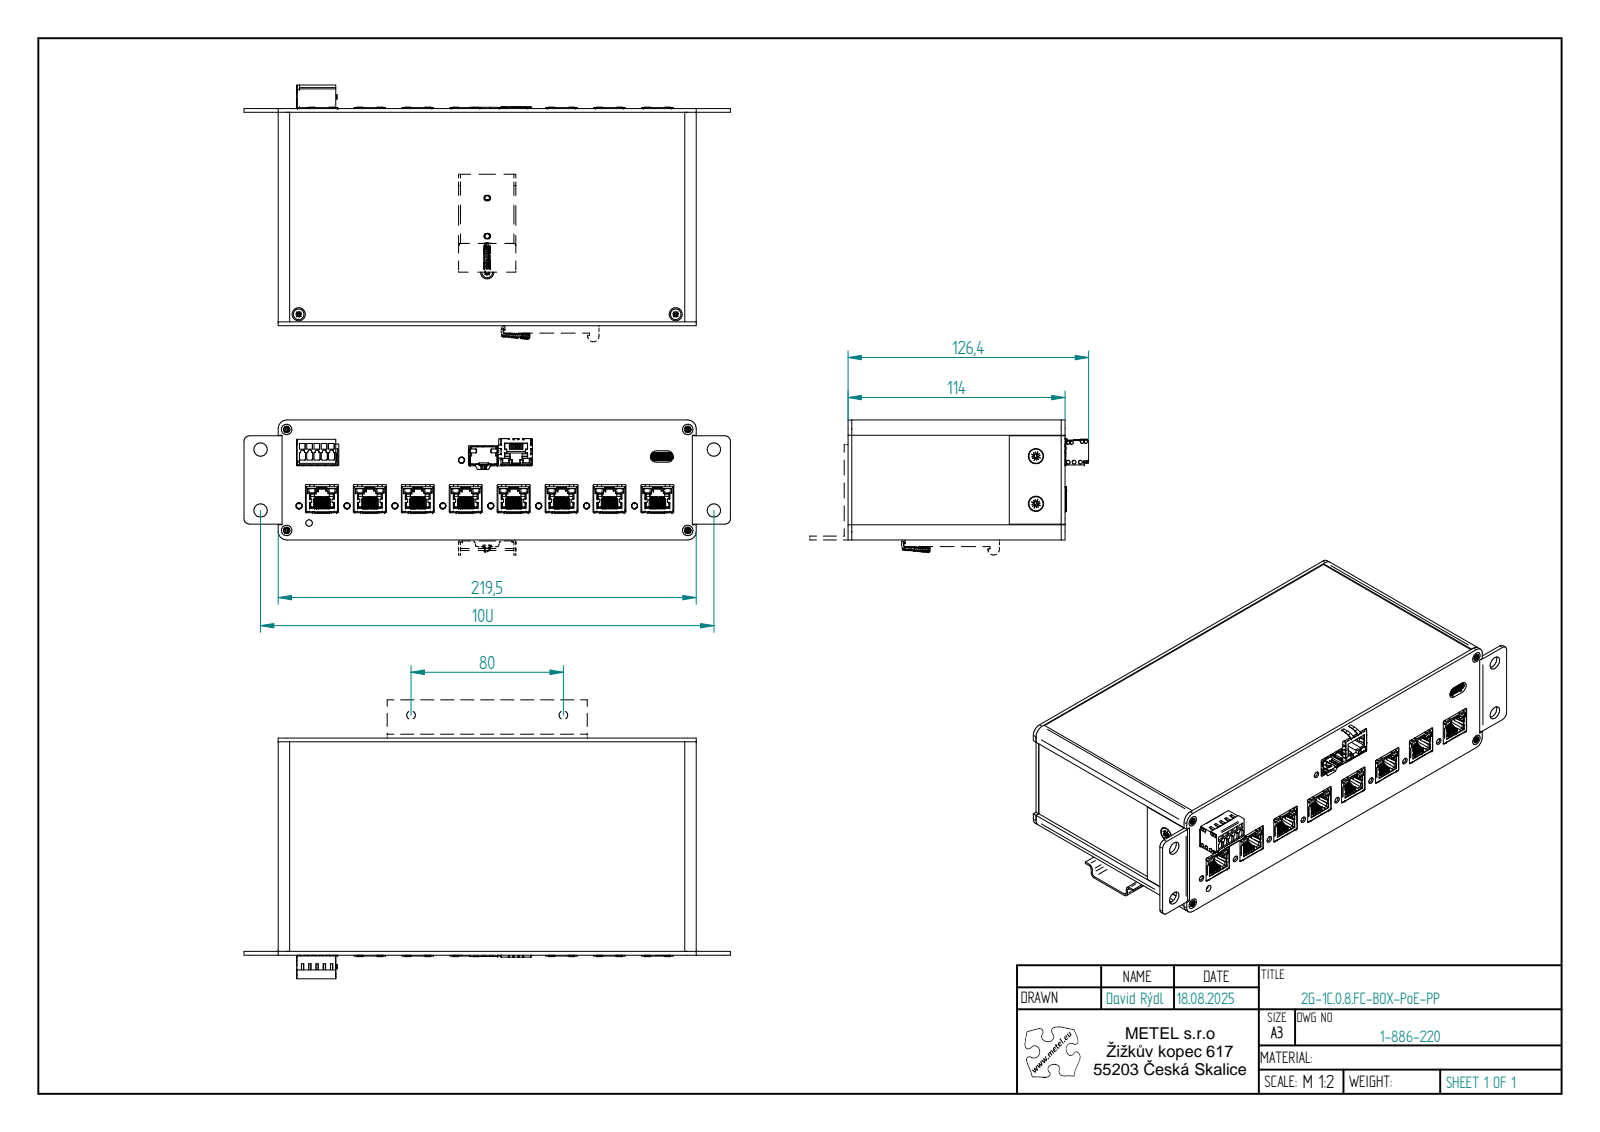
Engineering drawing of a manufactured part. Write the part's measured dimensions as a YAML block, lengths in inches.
part_name: "2G-1C.0.8.FC; Profil 210-2C.0.8-zak; 1-886-220-2G-1C.0.8.FC-Predni; 734-205 (+8 more)"
step_written_by: "Solid Edge (AUTOMOTIVE_DESIGN)"
units: inches
bodies: {solids: 69, faces: 14041, planar: 9493, cylindrical: 3379, other: 1169}
overall_size: [10.059, 5.762, 2.89]
volume: 17.13
surface_area: 387
round_holes:
  - {diameter: 0.039, count: 20}
  - {diameter: 0.079, count: 12}
  - {diameter: 0.13, count: 12}
  - {diameter: 0.126, count: 10}
  - {diameter: 0.138, count: 9}
  - {diameter: 0.097, count: 6}
  - {diameter: 0.059, count: 5}
  - {diameter: 0.018, count: 4}
  - {diameter: 0.106, count: 4}
  - {diameter: 0.276, count: 4}
  - {diameter: 0.016, count: 2}
  - {diameter: 0.02, count: 2}
round_bosses_or_shafts:
  - {diameter: 0.114, count: 12}
  - {diameter: 0.217, count: 4}
  - {diameter: 0.118, count: 4}
  - {diameter: 0.22, count: 3}
  - {diameter: 0.104, count: 3}
  - {diameter: 0.079, count: 3}
  - {diameter: 0.295, count: 2}
  - {diameter: 0.157, count: 2}
partial_cylinders:
  - {radius: 0.004, count: 167}
  - {radius: 0.008, count: 85}
  - {radius: 0.02, count: 84}
  - {radius: 0.012, count: 36}
  - {radius: 0.01, count: 32}
  - {radius: 0.039, count: 30}
  - {radius: 0.007, count: 28}
  - {radius: 0.005, count: 27}
face_to_face_distances: [0.113, 2.328, 0.079, 4.409, 2.441, 2.214, 0.157, 4.488, 4.331, 8.327]
hole_center_spacings: [0.991, 1.982, 2.973, 3.964, 2.973, 3.964, 4.955, 0.1]
